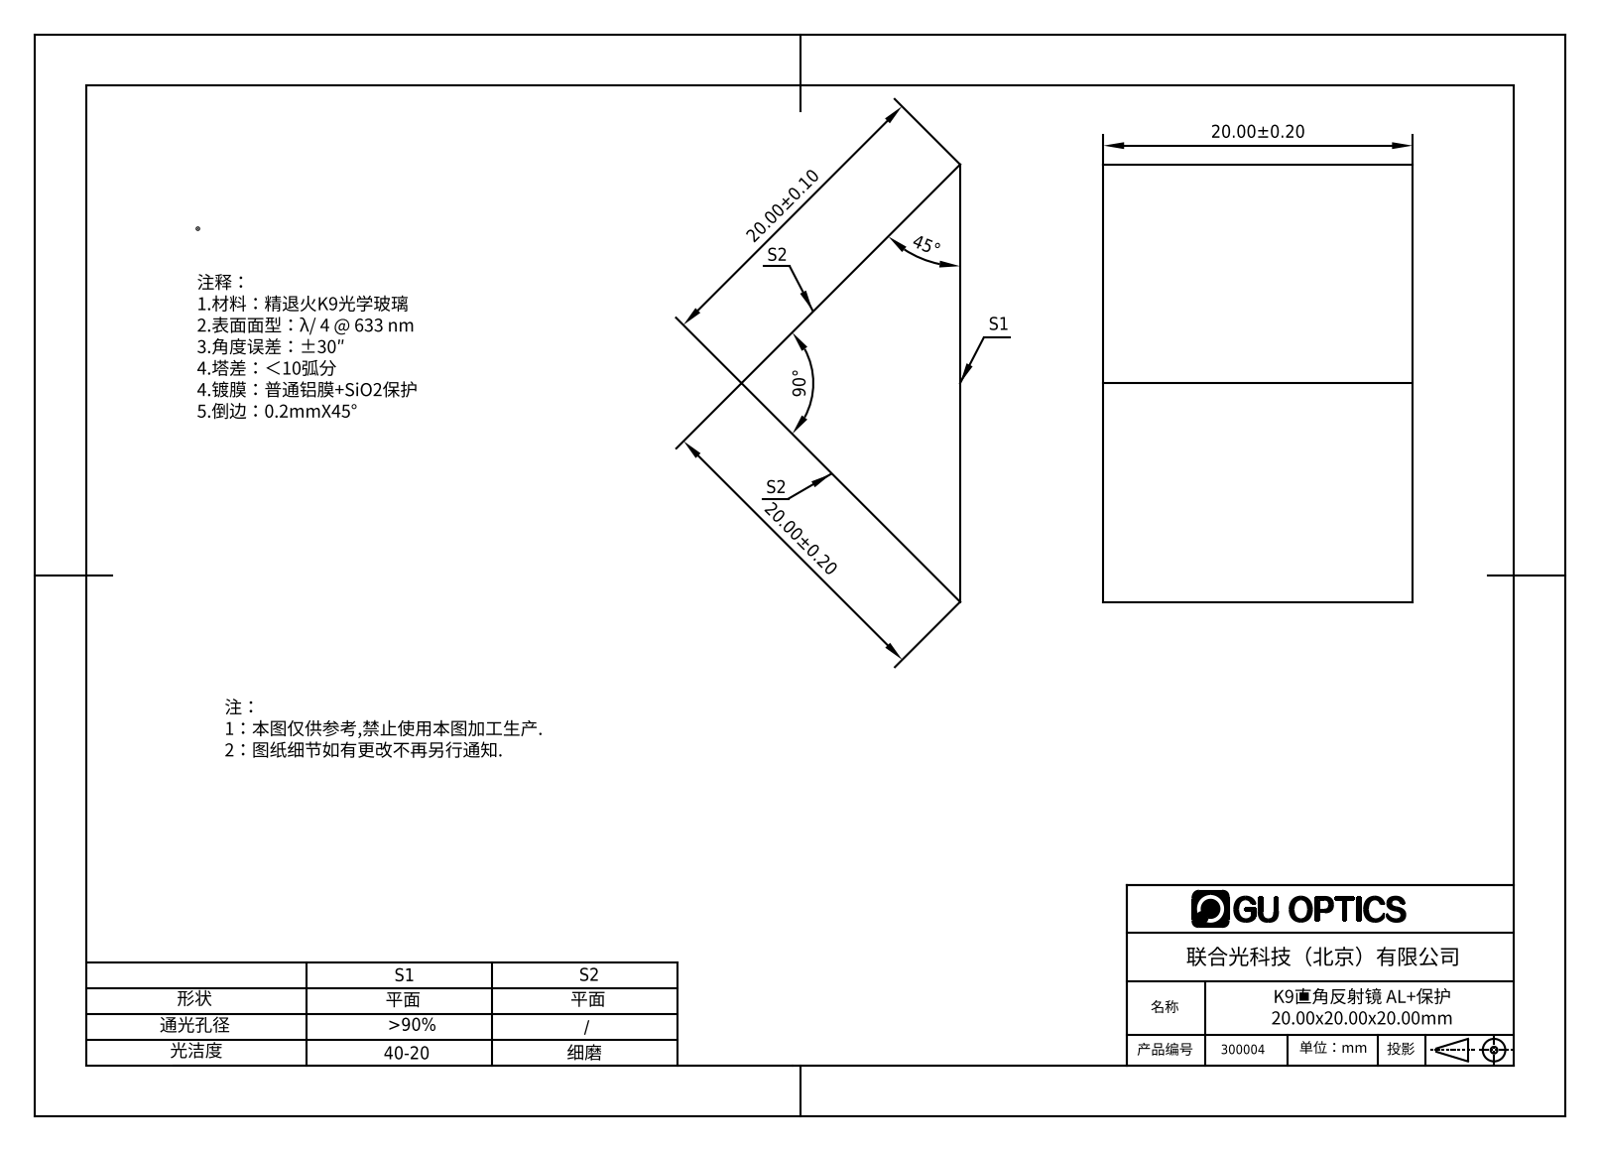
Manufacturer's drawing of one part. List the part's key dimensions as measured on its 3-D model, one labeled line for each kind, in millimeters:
Part name (STEP PRODUCT): 30004
STEP written by: SolidWorks 2016 (AUTOMOTIVE_DESIGN)
Units: millimetres
Bodies: 1 solid, 5 faces (5 planar, 0 cylindrical, 0 other)
Overall size (bounding box): 28.28 × 20 × 14.14
Volume: 4 000 mm³ · Surface area: 1 766 mm²
Main face-to-face distances: 20
